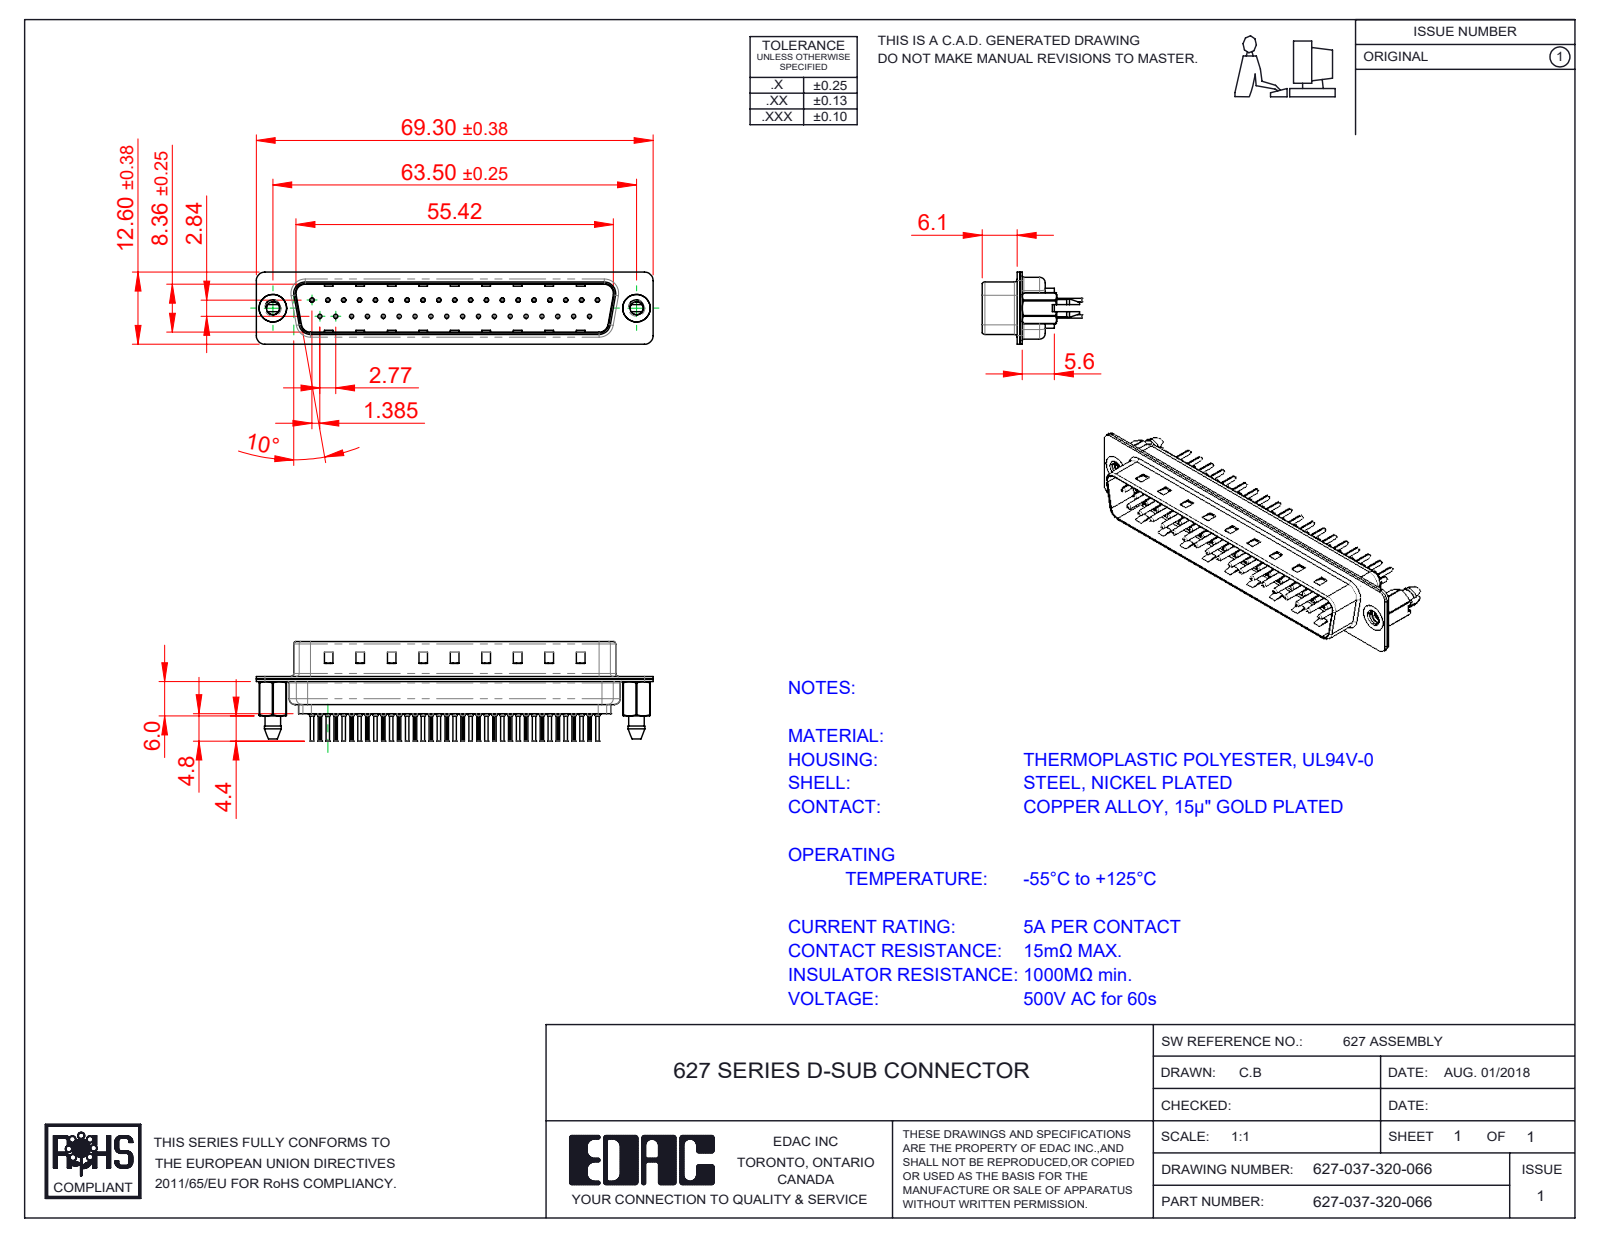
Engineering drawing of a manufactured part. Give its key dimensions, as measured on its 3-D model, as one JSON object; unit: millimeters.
{"part_name": "627 Shell Rear_37 Contacts; 627 4-40 Threaded Boardlock_LP; 627 Shell Front_37 Contacts; 627 Contact Row 2_20L (+3 more)", "step_written_by": "SolidWorks 2020 (CONFIG_CONTROL_DESIGN)", "units": "millimeters", "bodies": {"solids": 42, "faces": 4112, "planar": 1123, "cylindrical": 1542, "other": 1447}, "overall_size": [69.3, 17.3, 12.6], "volume_mm3": 3816, "surface_area_mm2": 10972, "round_holes": [[0.2, 37], [0.35, 37], [1.1, 37], [1.6, 37], [2.26, 2], [4, 2], [4.8, 2]], "round_bosses_or_shafts": [[2, 37], [1.5, 37], [0.75, 37], [0.6, 37], [4.9, 2]], "partial_cylinders_radius": [[0.1, 74], [1.5, 18], [2, 12], [1.6, 10], [0.5, 8], [0.25, 4], [0.6, 4], [0.65, 4]], "face_to_face_distances": [0.4, 0.82, 9.58, 0.45, 8.76, 1.5, 0.9, 1.4, 6.5, 6.05], "hole_center_spacings": [3.16, 2.77, 5.54, 8.31, 5.04, 10.1, 11.08, 12.78]}
